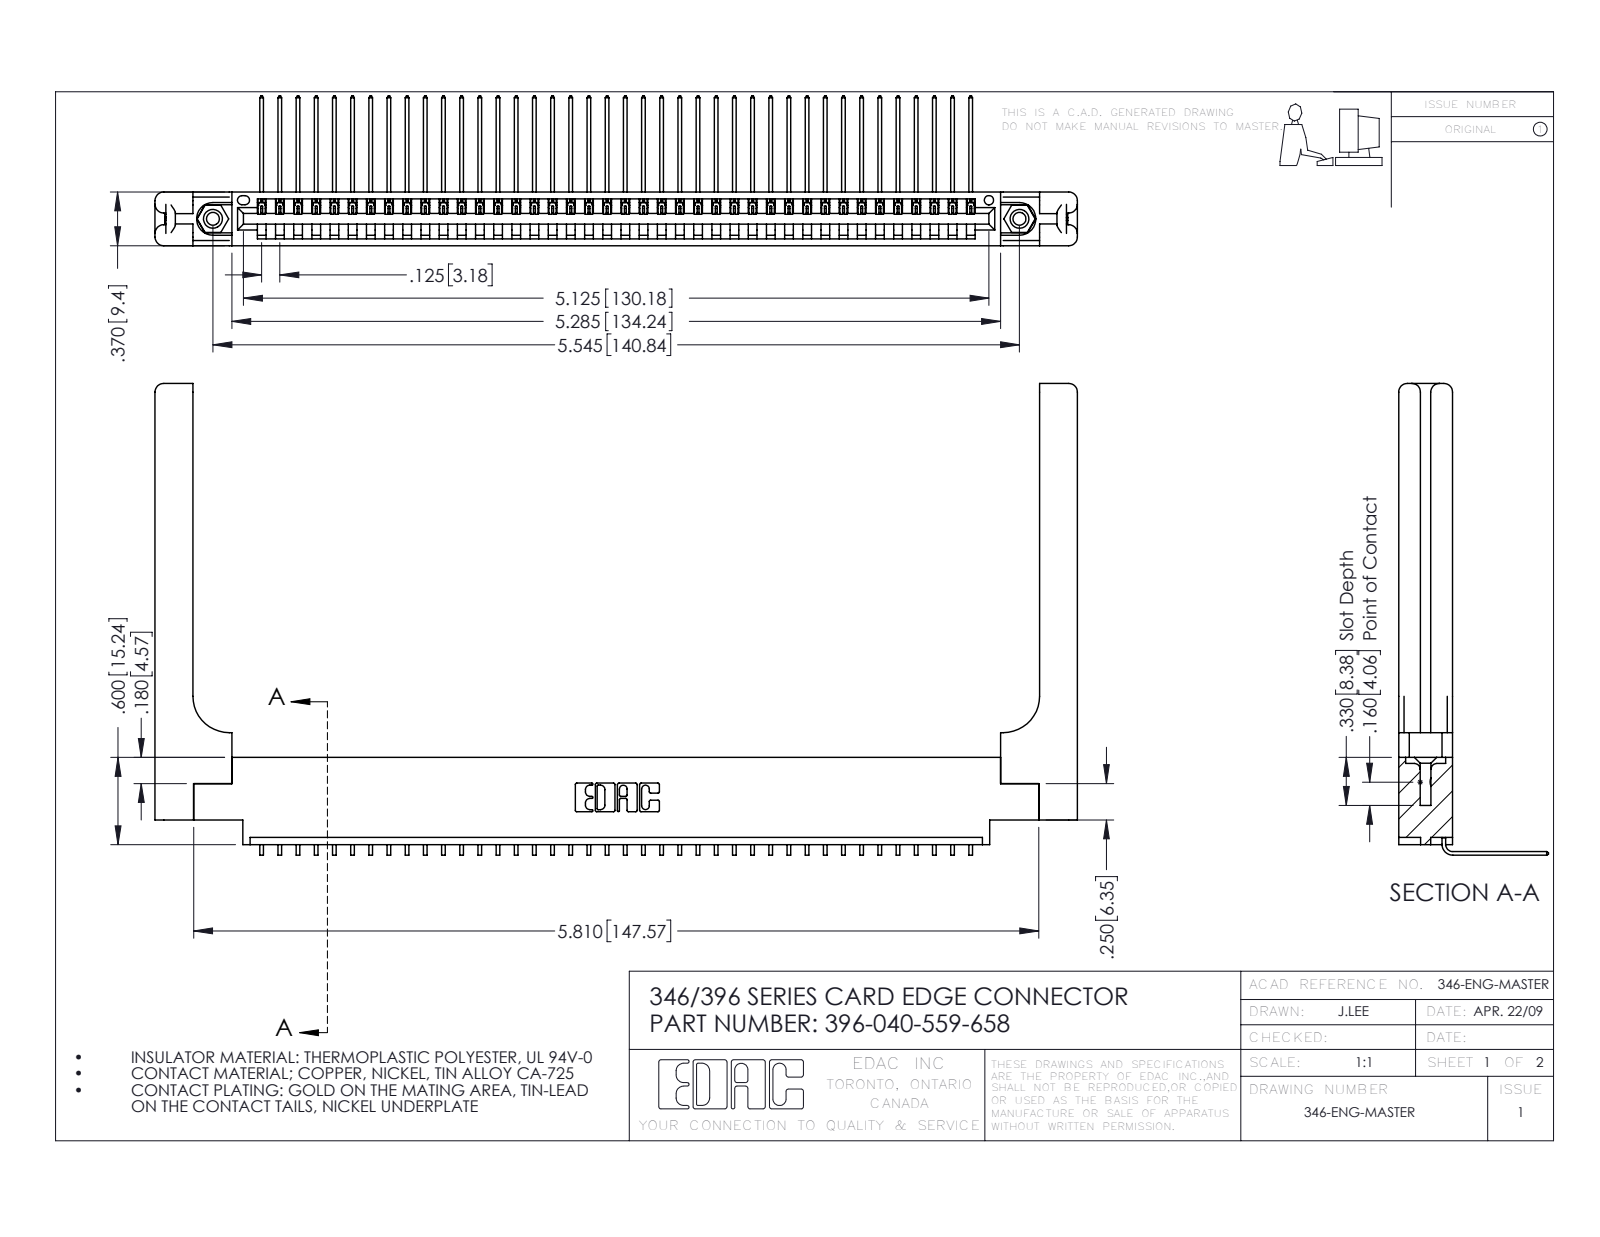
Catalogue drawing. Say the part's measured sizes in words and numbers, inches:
The part is named "346-220-058_345-220-058; 346 Part_0.170 Offset - 0.156 Dia-TH; 396-040-559-658; 345-250-001_345-250-001-102 (+1 more)". Its 3-D file was written by "SolidWorks 2016 (CONFIG_CONTROL_DESIGN)". It is 45 solids with 2782 faces: 1908 planar, 814 cylindrical and 60 other. Overall it measures 6.341 by 3.243 by 1.03 inches. Its volume is 1.397 cubic inches and its surface area 39.26 square inches. Round holes: 2 of diameter 0.089, 2 of diameter 0.125, 2 of diameter 0.156, 1 of diameter 0.064. Round bosses or shafts: 2 of diameter 0.155. Partial cylindrical surfaces (rounded edges, fillets, slot ends): 80 of radius 0.006, 22 of radius 0.01, 16 of radius 0.06, 6 of radius 0.007, 6 of radius 0.031, 3 of radius 0.026, 2 of radius 0.03, 2 of radius 0.031. The main face-to-face distances are 0.37, 0.048, 0.072, 0.322, 0.148, 0.15, 0.025, 0.25, 0.298, 0.222. The hole center spacings are 0.246, 5.336, 5.545.
